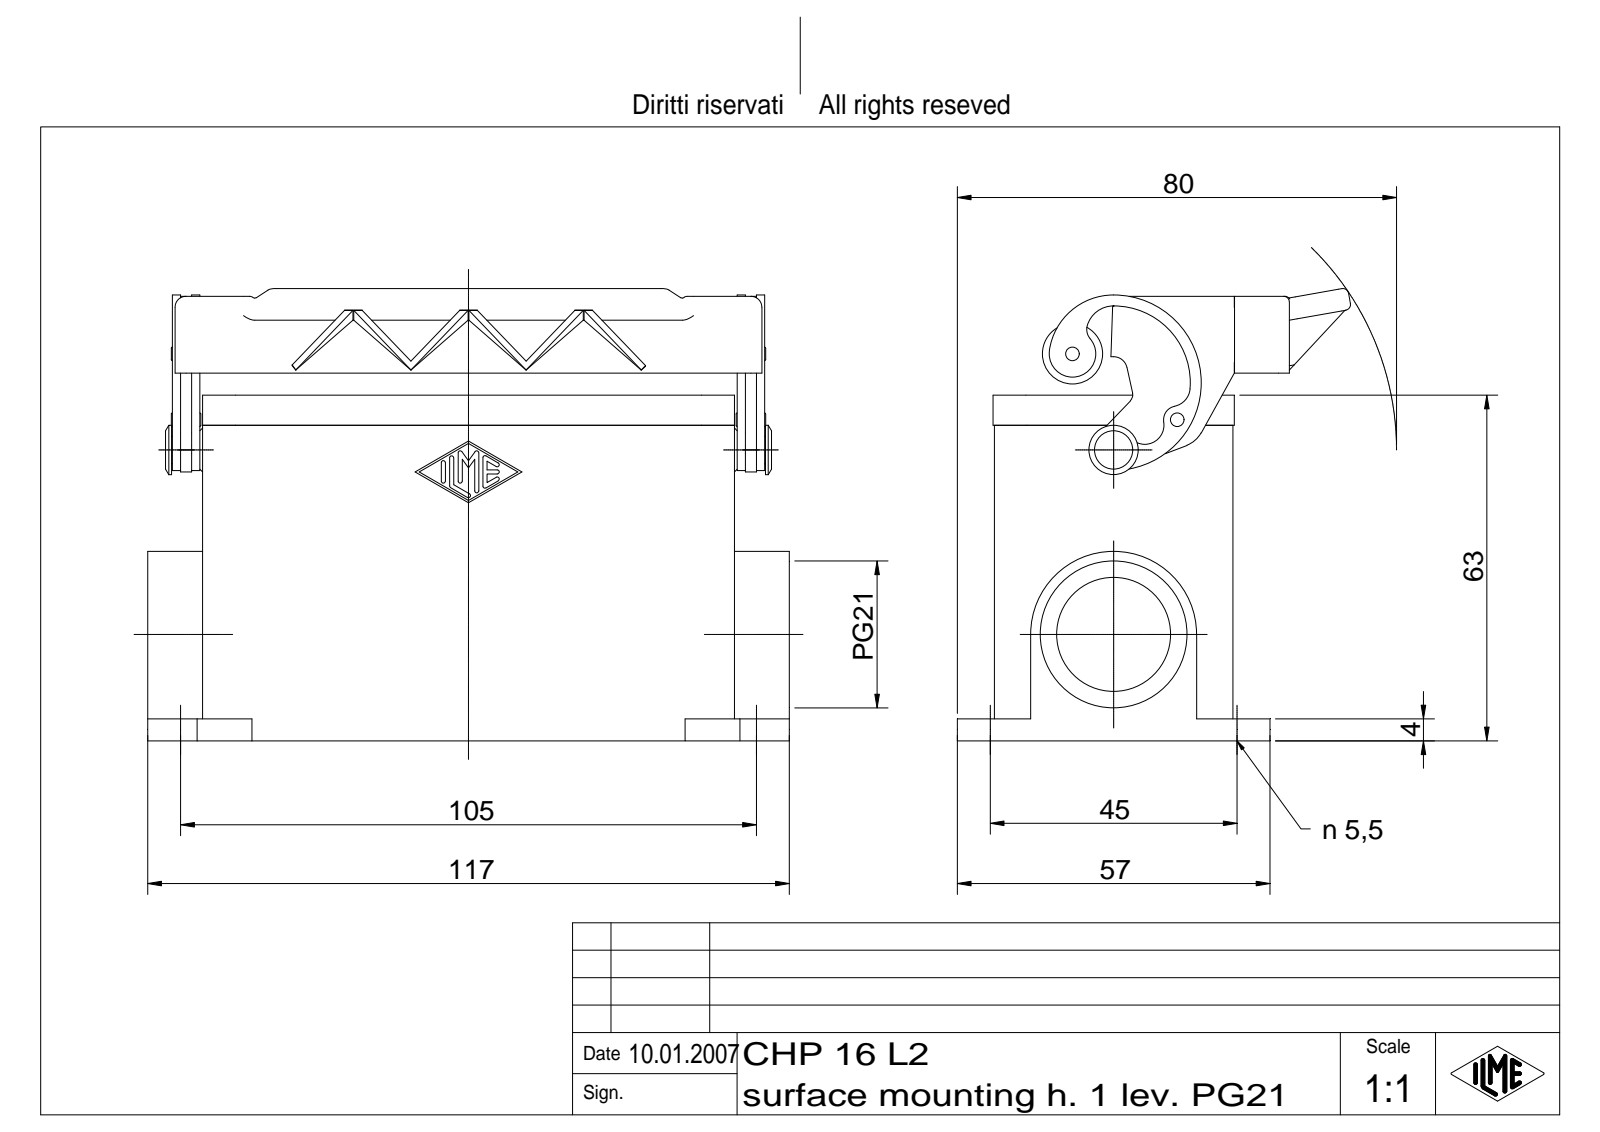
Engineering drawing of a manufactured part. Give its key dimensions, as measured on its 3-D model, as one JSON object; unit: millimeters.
{"part_name": "CHP 16 L2", "step_written_by": "Autodesk Inventor 7 (AUTOMOTIVE_DESIGN)", "units": "millimeters", "bodies": {"solids": 4, "faces": 449, "planar": 177, "cylindrical": 123, "other": 149}, "overall_size": [117, 82.42, 71.7], "volume_mm3": 108925, "surface_area_mm2": 58959, "round_holes": [[5.5, 4], [2, 1], [20.78, 1], [26.78, 1]], "round_bosses_or_shafts": [[11, 1], [9, 1], [5, 1], [3, 1], [2.5, 1]], "partial_cylinders_radius": [[0.38, 14], [2, 12], [6, 8], [1, 7], [1.5, 5], [3, 4], [2.5, 3], [3.5, 2]], "face_to_face_distances": [3, 40.5, 4, 43.5, 37.5, 57.5, 53.5, 13.25, 83.75, 63], "hole_center_spacings": [45, 105, 114.24, 40.79]}
